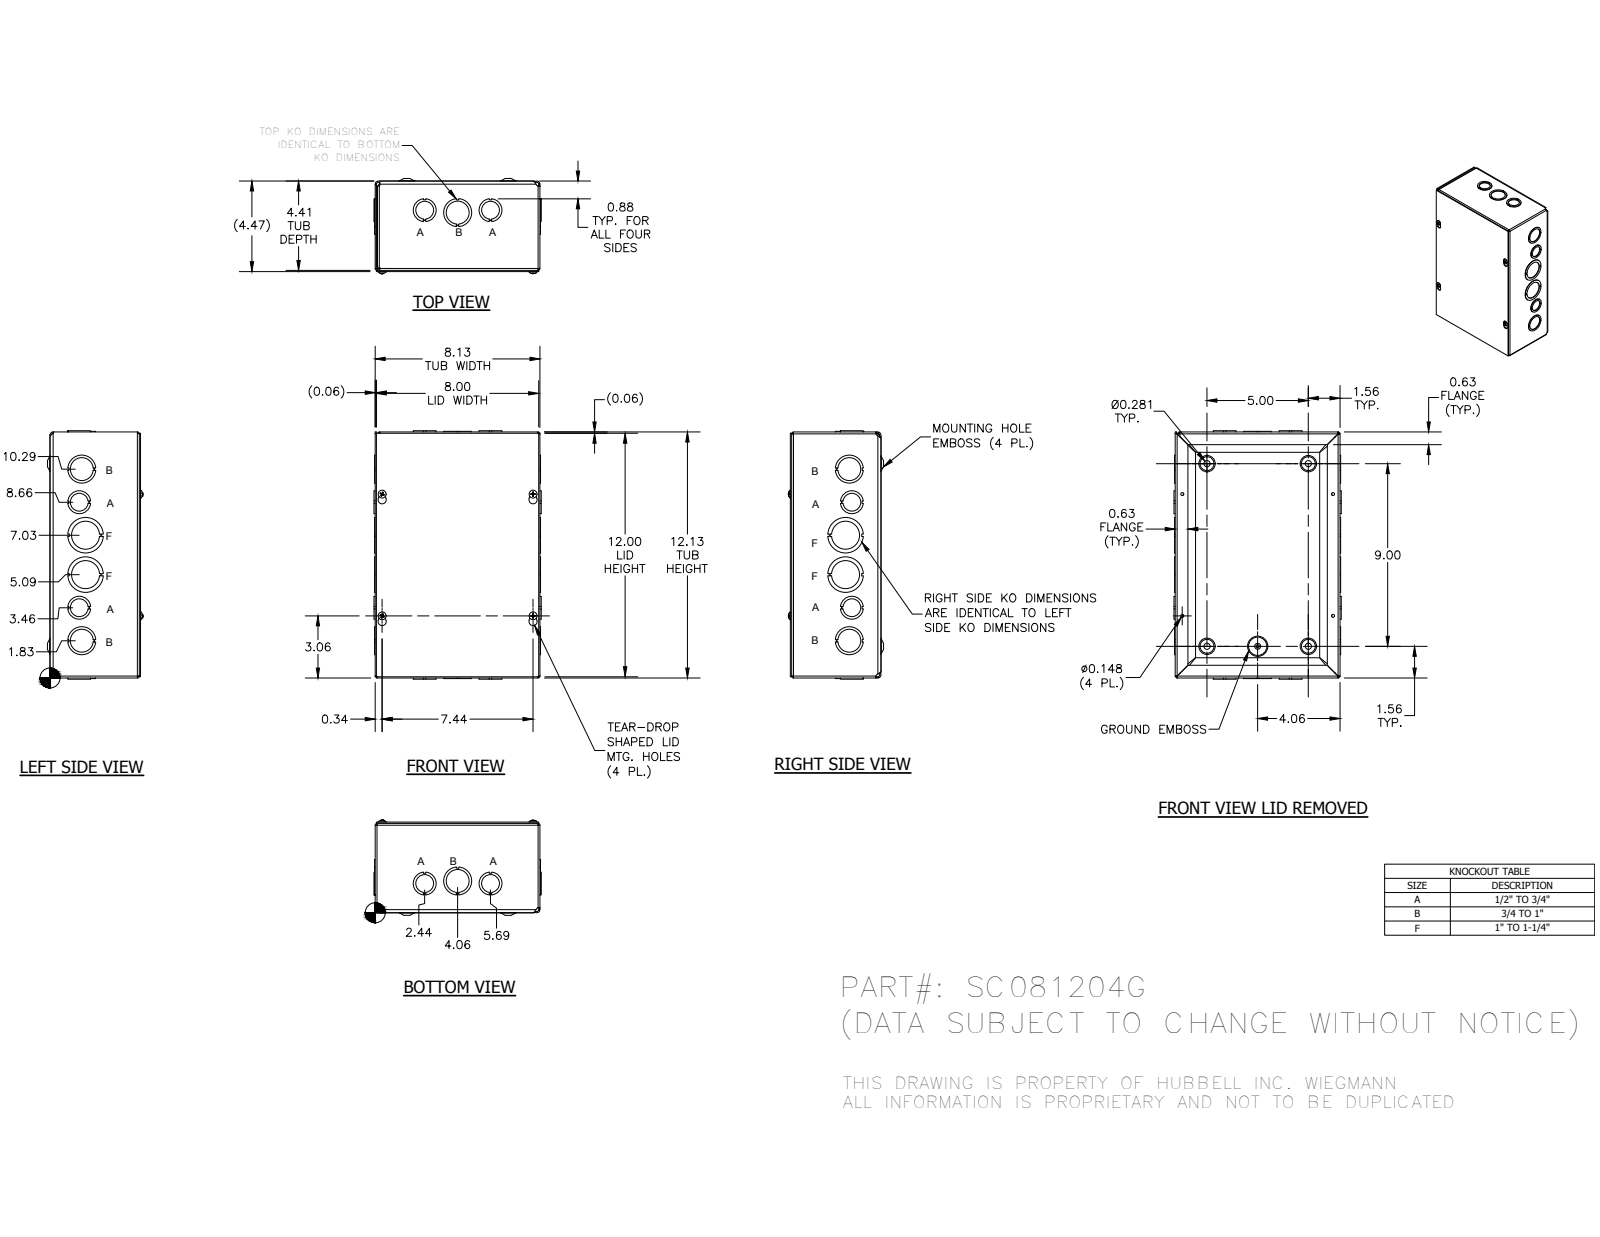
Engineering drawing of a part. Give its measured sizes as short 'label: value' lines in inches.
name: SC0812GBKP; SC081204GWRA; SC0812GLID; 34056 (+1 more)
written by: Autodesk Inventor 2014 (AUTOMOTIVE_DESIGN)
unit: in
bodies: 22 solids, 862 faces (530 planar, 181 cylindrical, 151 other)
size: 12.249 × 8.249 × 4.693
holes: 7× ⌀1.125, 5× ⌀1.375, 4× ⌀0.148, 4× ⌀0.3, 4× ⌀0.875, 2× ⌀1.75, 1× ⌀0.165
bosses: 4× ⌀0.384, 4× ⌀0.164, 1× ⌀0.228
rounds: 8× R0.031, 8× R0.093, 4× R0.055, 4× R0.062, 4× R0.094, 4× R0.11, 4× R0.117, 4× R0.124
face distances: 0.062, 4.343, 4.405, 0.063, 4.406, 4.468, 0.062, 12.063, 8.125, 8.063
hole spacings: 1.933, 7.598, 1.635, 1.659, 2.5, 3.265, 3.584, 4.01
